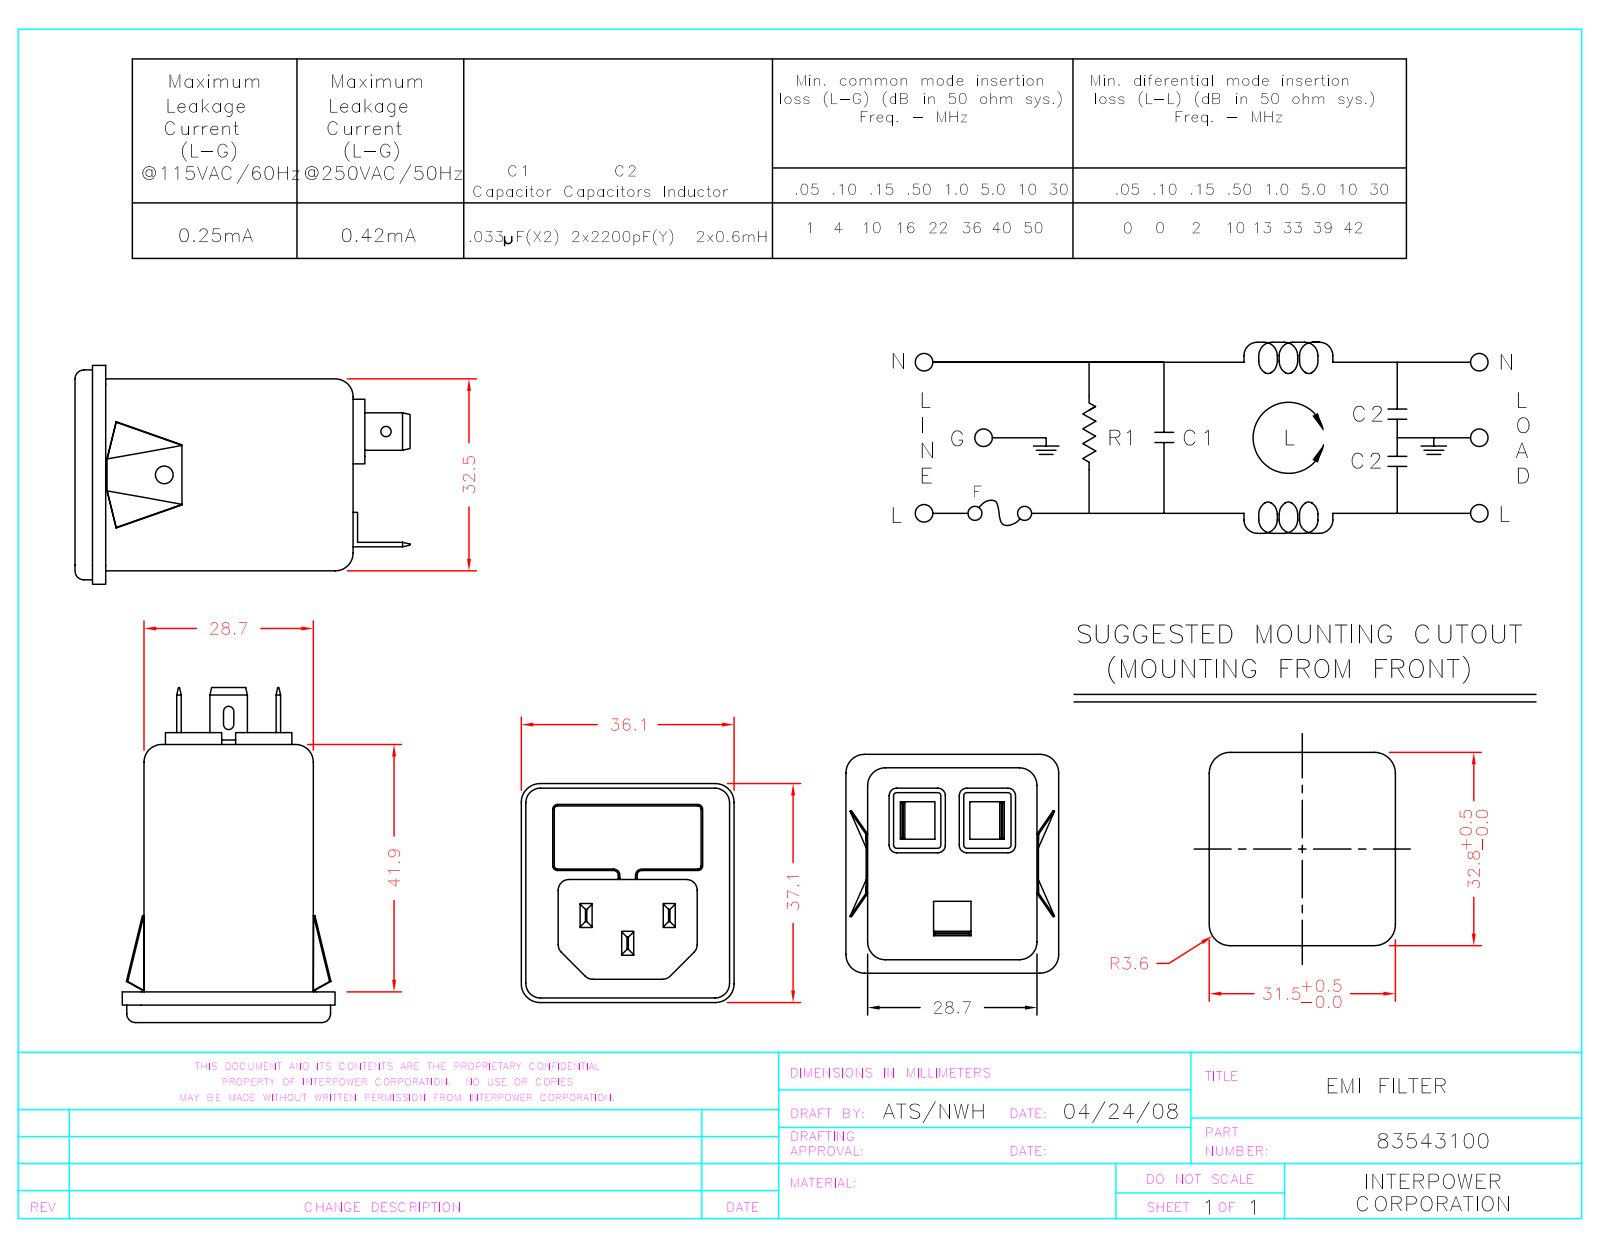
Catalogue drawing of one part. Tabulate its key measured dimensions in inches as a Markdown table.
| quantity | value |
| --- | --- |
| part name | 6EGS1-1 |
| STEP written by | SolidWorks 2008 (CONFIG_CONTROL_DESIGN) |
| units | inches |
| bodies | 1 solid, 250 faces (163 planar, 73 cylindrical, 14 other) |
| overall size | 2.235 × 1.46 × 1.42 |
| volume | 2.417 in³ |
| surface area | 17.84 in² |
| round holes (diameter × count) | 0.069 × 1, 0.118 × 1 |
| partial cylindrical surfaces (radius × count) | 0.02 × 8, 0.05 × 8, 0.118 × 8, 0.01 × 6, 0.031 × 6, 0.071 × 6, 0.021 × 4, 0.059 × 4 |
| main face-to-face distances | 1.13, 1.28, 1.855, 1.65, 0.205, 0.55, 1.205, 0.445, 0.65, 0.731 |
| hole center spacings | 1.507 |
